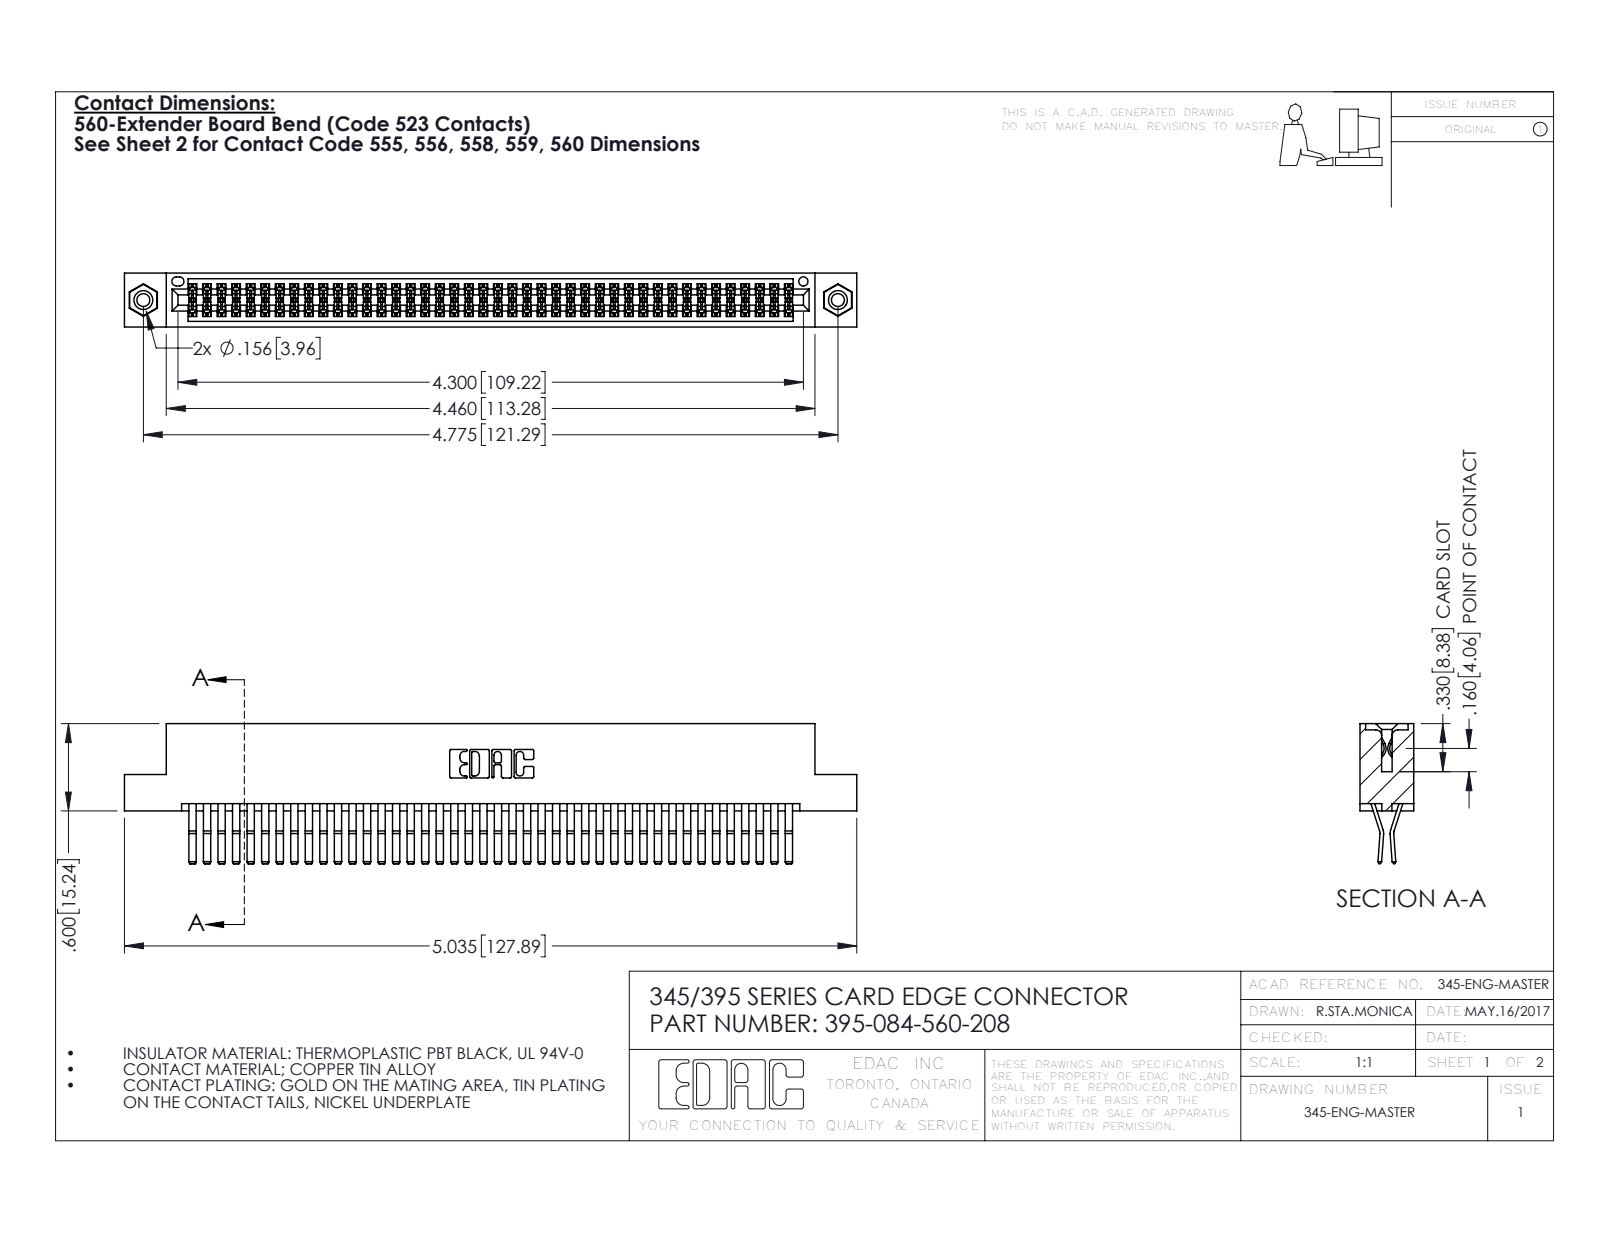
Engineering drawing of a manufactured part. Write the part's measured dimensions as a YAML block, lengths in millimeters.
part_name: "345 Part_Flush Mounting Lugs - 0.156 Dia-TI; 345-250-001_345-250-003-102; 345-292-001_560 Tail; 395-084-560-208"
step_written_by: "SolidWorks 2016 (CONFIG_CONTROL_DESIGN)"
units: millimeters
bodies: {solids: 87, faces: 4554, planar: 2884, cylindrical: 1654, other: 16}
overall_size: [127.9, 24.4, 9.4]
volume: 13000
surface_area: 20600
round_holes:
  - {diameter: 2.3, count: 2}
  - {diameter: 3.2, count: 2}
  - {diameter: 4, count: 2}
  - {diameter: 1.6, count: 1}
round_bosses_or_shafts:
  - {diameter: 3.9, count: 2}
partial_cylinders:
  - {radius: 0.2, count: 126}
  - {radius: 0.3, count: 22}
  - {radius: 0.2, count: 6}
  - {radius: 0.8, count: 6}
  - {radius: 0.7, count: 3}
  - {radius: 0.3, count: 2}
  - {radius: 0.4, count: 2}
  - {radius: 0.5, count: 2}
face_to_face_distances: [0.6, 1.8, 7.6, 5.1, 9.4, 2.5, 6.9, 5.7, 4.4, 3.8]
hole_center_spacings: [6.9, 115.3, 121.3]
